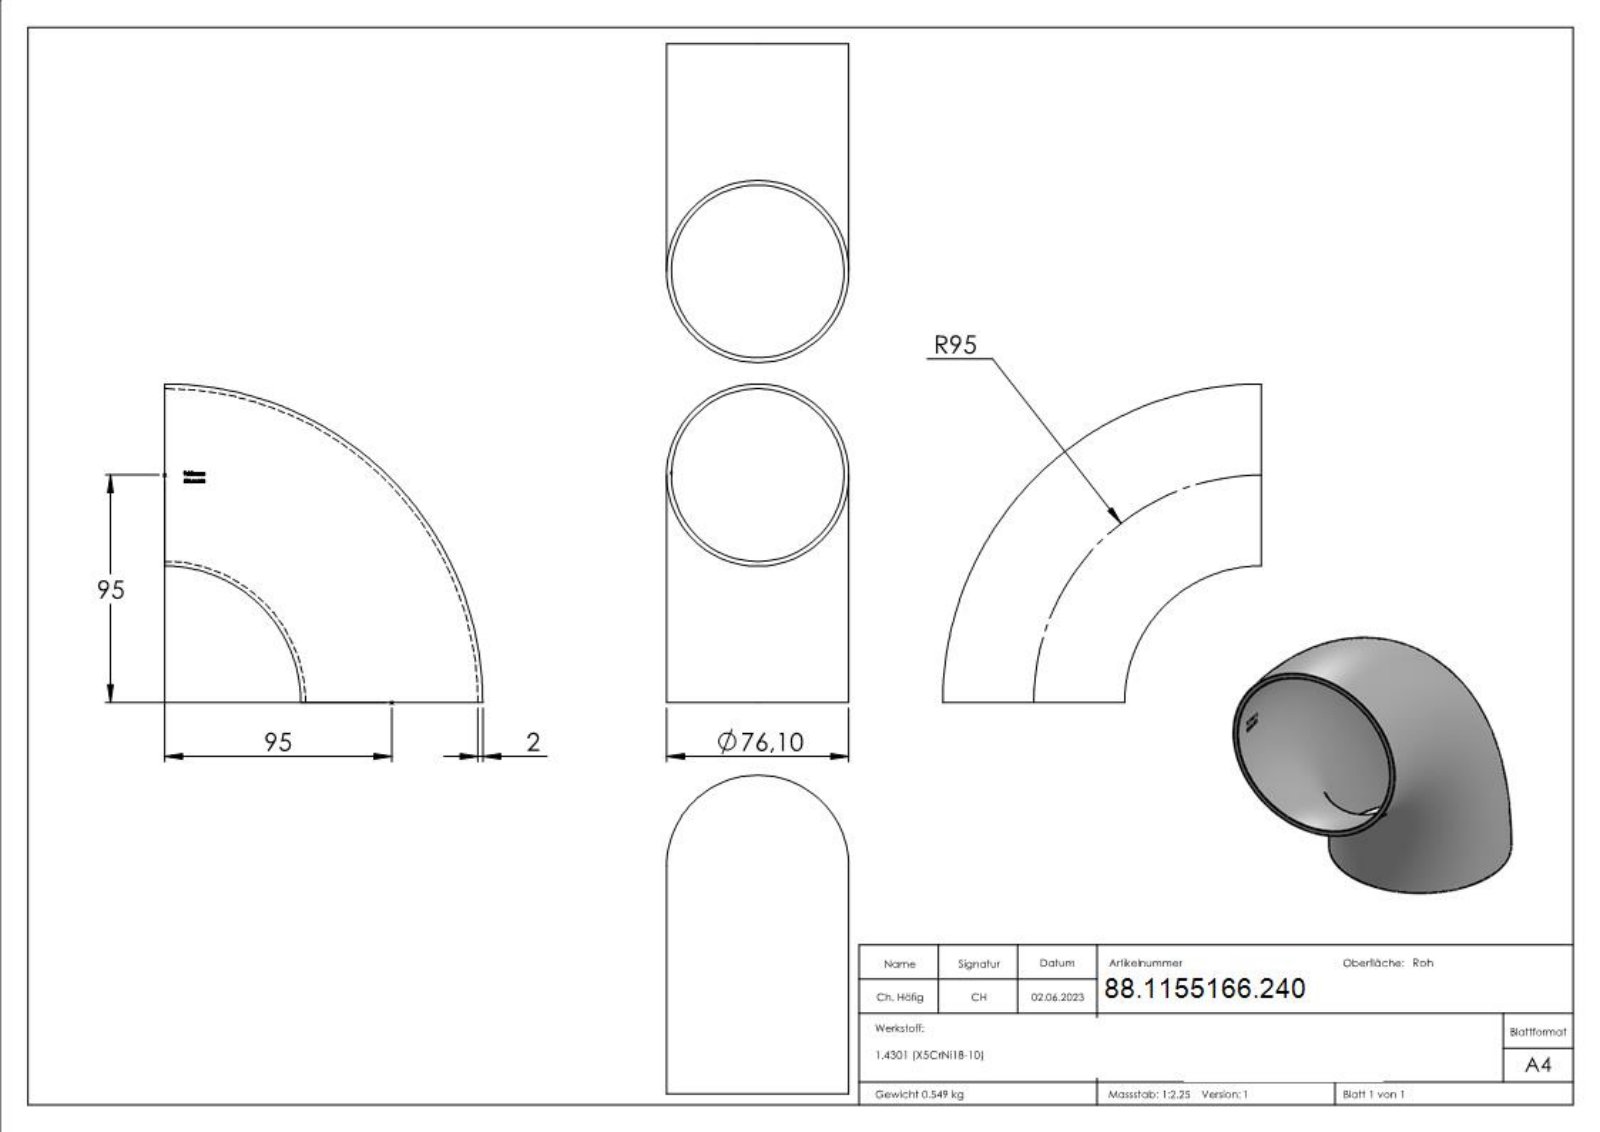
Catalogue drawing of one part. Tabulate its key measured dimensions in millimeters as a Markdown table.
| quantity | value |
| --- | --- |
| part name | 55166-240 |
| STEP written by | SolidWorks 2018 (CONFIG_CONTROL_DESIGN) |
| units | millimeters |
| bodies | 1 solid, 226 faces (103 planar, 0 cylindrical, 123 other) |
| overall size | 133.05 × 133.05 × 76.1 |
| volume | 69 477 mm³ |
| surface area | 70 418 mm² |
| main face-to-face distances | 0.39, 1.26, 2.97, 1.32, 4.23, 0.99, 2.02, 0.87, 3.66, 0.74 |
